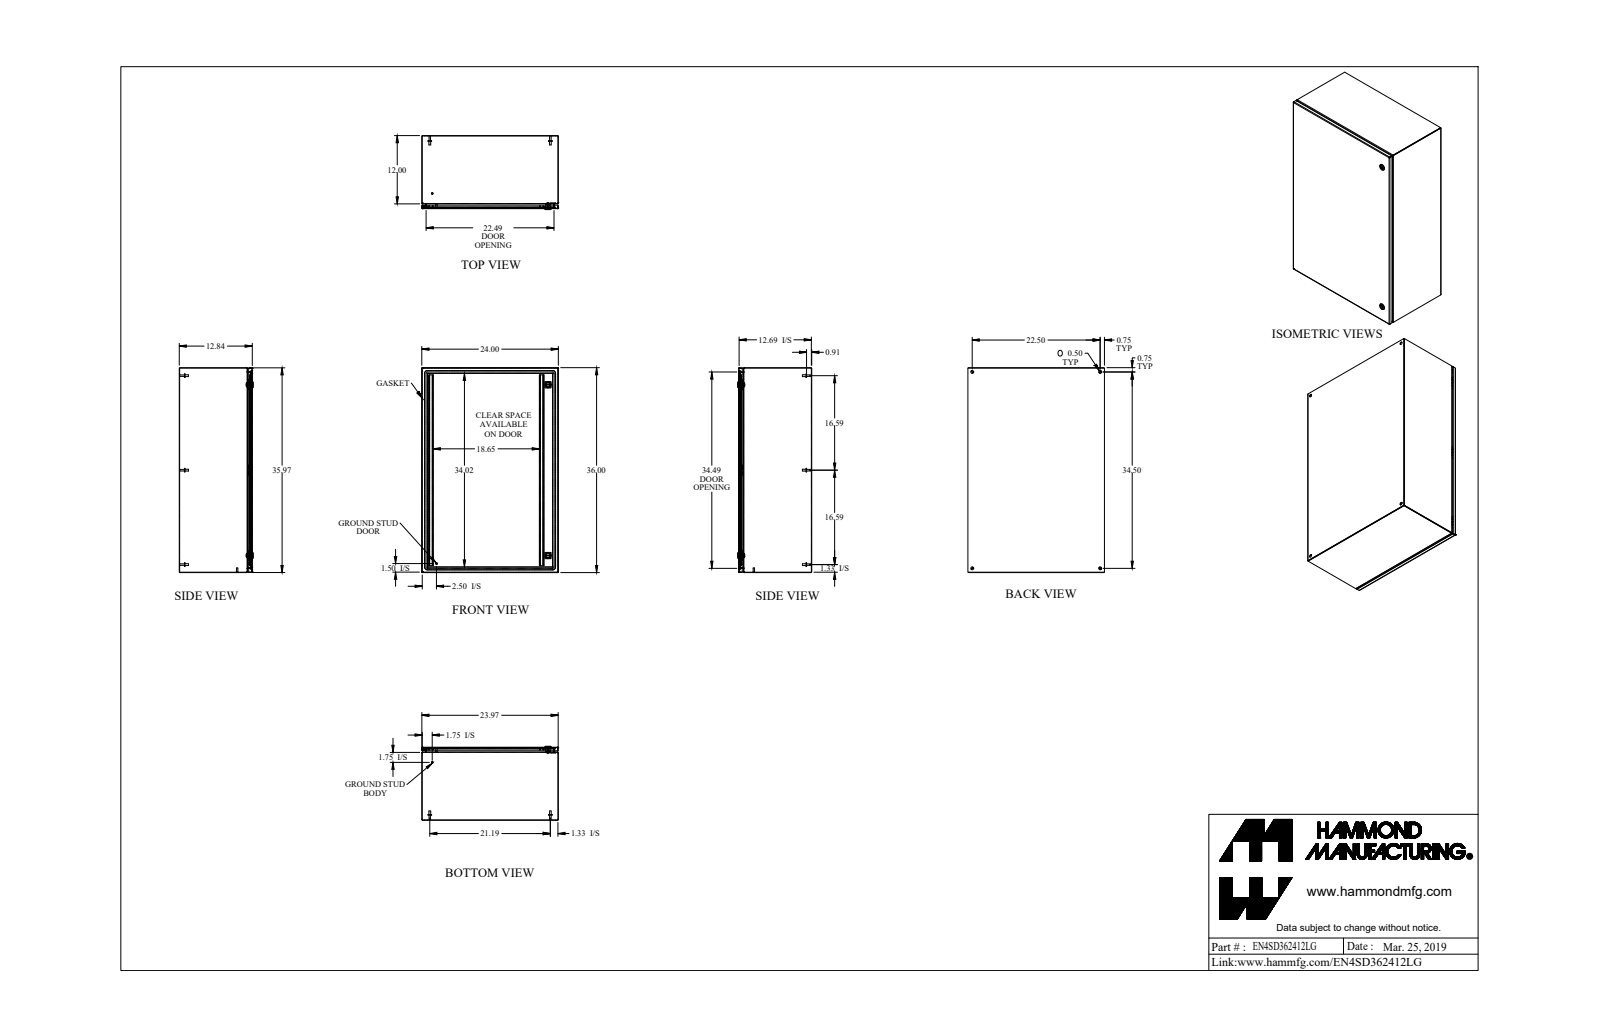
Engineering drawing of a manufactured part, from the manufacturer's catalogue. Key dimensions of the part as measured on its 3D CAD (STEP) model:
Part name (STEP PRODUCT): EN4SD362412LG
STEP written by: SolidWorks 2019 (AUTOMOTIVE_DESIGN)
Units: inches
Bodies: 35 solids, 901 faces (434 planar, 295 cylindrical, 172 other)
Overall size (bounding box): 36 × 24 × 12.997
Volume: 261.1 in³ · Surface area: 7 334 in²
Round holes (diameter × count): ⌀0.5 ×4, ⌀0.232 ×2, ⌀0.625 ×2, ⌀0.785 ×2, ⌀0.172 ×1, ⌀0.24 ×1, ⌀0.242 ×1
Round bosses / shafts (diameter × count): ⌀0.625 ×6, ⌀0.313 ×6, ⌀0.27 ×6, ⌀1.1 ×2, ⌀0.525 ×2, ⌀0.281 ×2, ⌀0.25 ×2, ⌀0.455 ×1
Partial cylindrical surfaces — rounded edges, fillets, slot ends (radius × count): R0.036 ×18, R0.108 ×18, R0.043 ×12, R0.081 ×12, R0.312 ×12, R0.006 ×6, R0.062 ×6, R0.125 ×4
Main face-to-face distances: 0.072, 12.765, 12.693, 12.837, 23.928, 35.928, 23.856, 24, 35.856, 36
Hole centre spacings: 22.5, 34.5, 41.189, 2.493, 2.494, 21.544, 21.545, 29.999
